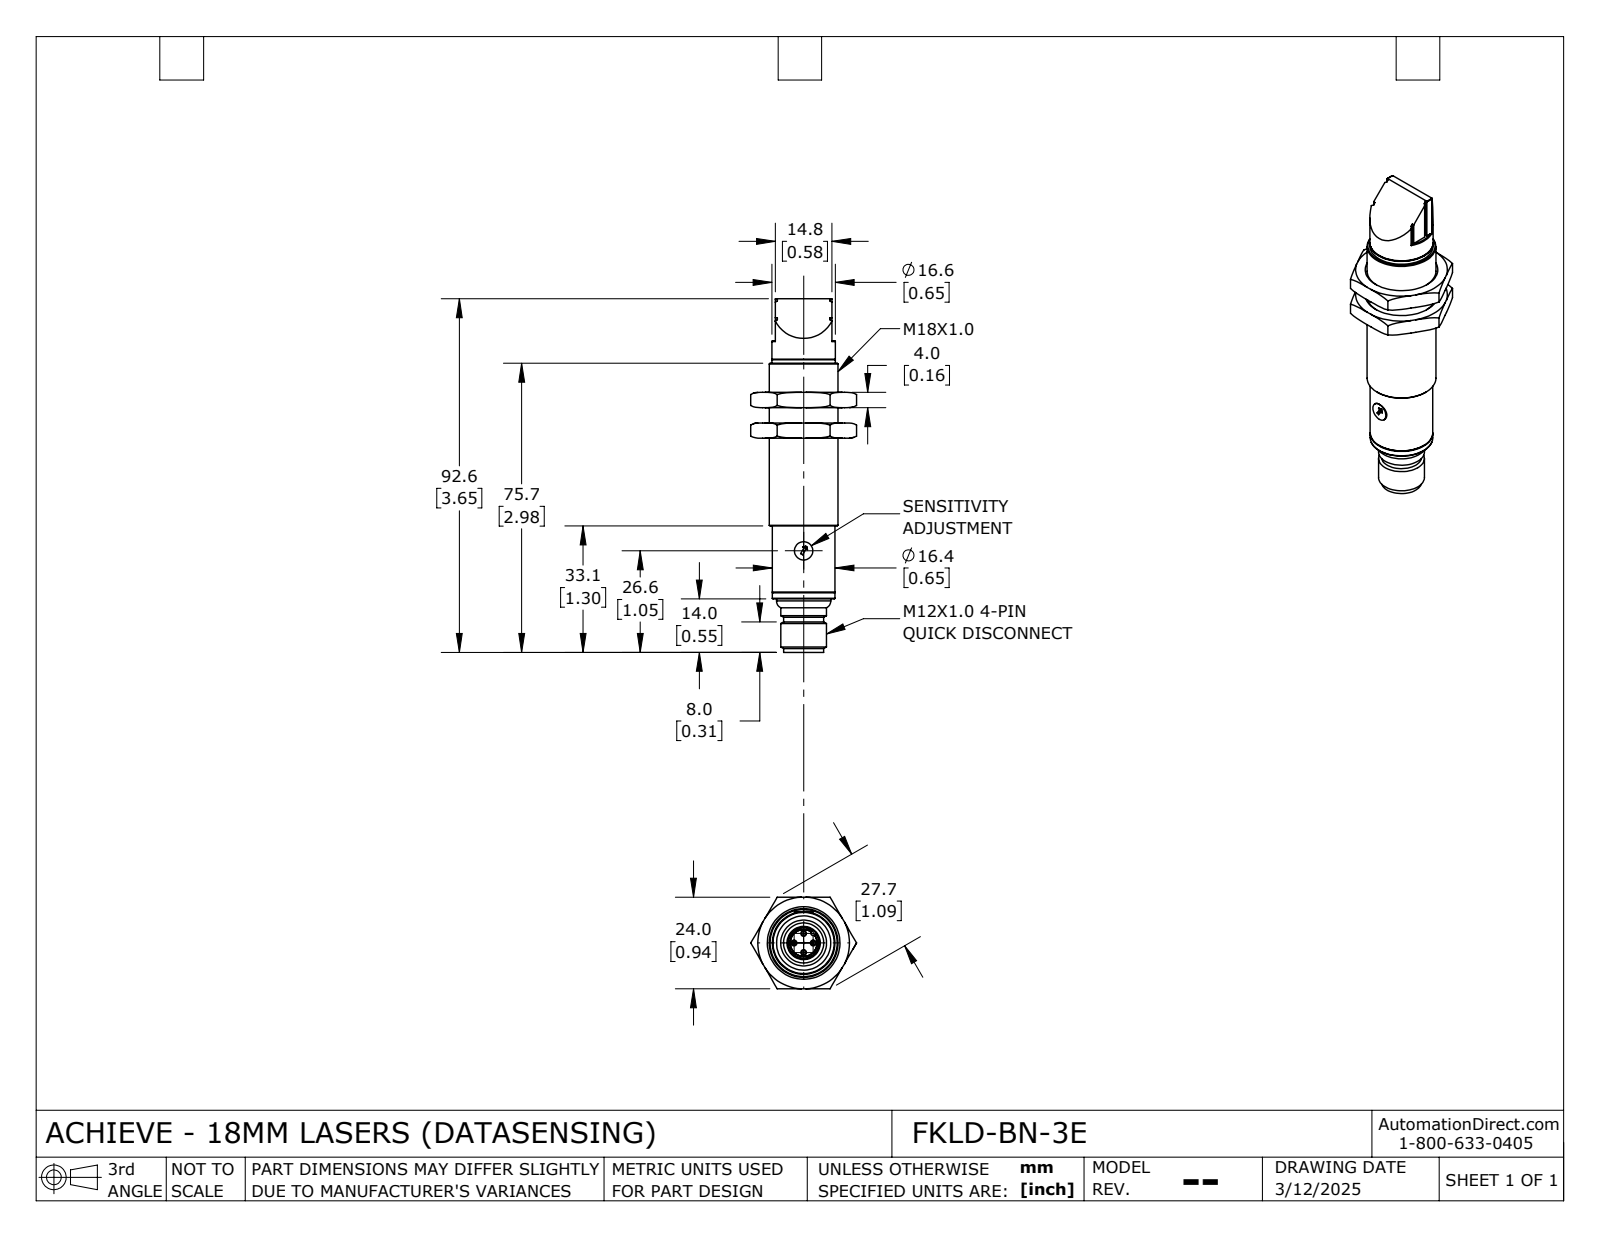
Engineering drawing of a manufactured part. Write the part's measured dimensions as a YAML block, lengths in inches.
part_name: "FKLD-BN-3E_Default"
step_written_by: "SolidWorks 2024 (CONFIG_CONTROL_DESIGN)"
units: inches
bodies: {solids: 3, faces: 156, planar: 73, cylindrical: 31, other: 52}
overall_size: [3.646, 1.091, 0.945]
volume: 1.243
surface_area: 12.62
round_holes:
  - {diameter: 0.278, count: 1}
  - {diameter: 0.327, count: 1}
  - {diameter: 0.583, count: 1}
  - {diameter: 0.709, count: 1}
round_bosses_or_shafts:
  - {diameter: 0.039, count: 4}
  - {diameter: 0.654, count: 1}
  - {diameter: 0.646, count: 1}
  - {diameter: 0.559, count: 1}
  - {diameter: 0.472, count: 1}
  - {diameter: 0.413, count: 1}
  - {diameter: 0.276, count: 1}
  - {diameter: 0.189, count: 1}
partial_cylinders:
  - {radius: 0.004, count: 2}
  - {radius: 0.02, count: 2}
  - {radius: 0.297, count: 2}
  - {radius: 0.024, count: 1}
  - {radius: 0.053, count: 1}
face_to_face_distances: [0.157, 0.315, 0.945, 0.473, 0.481, 0.788, 0.796, 0.631, 0.639, 0.472]
